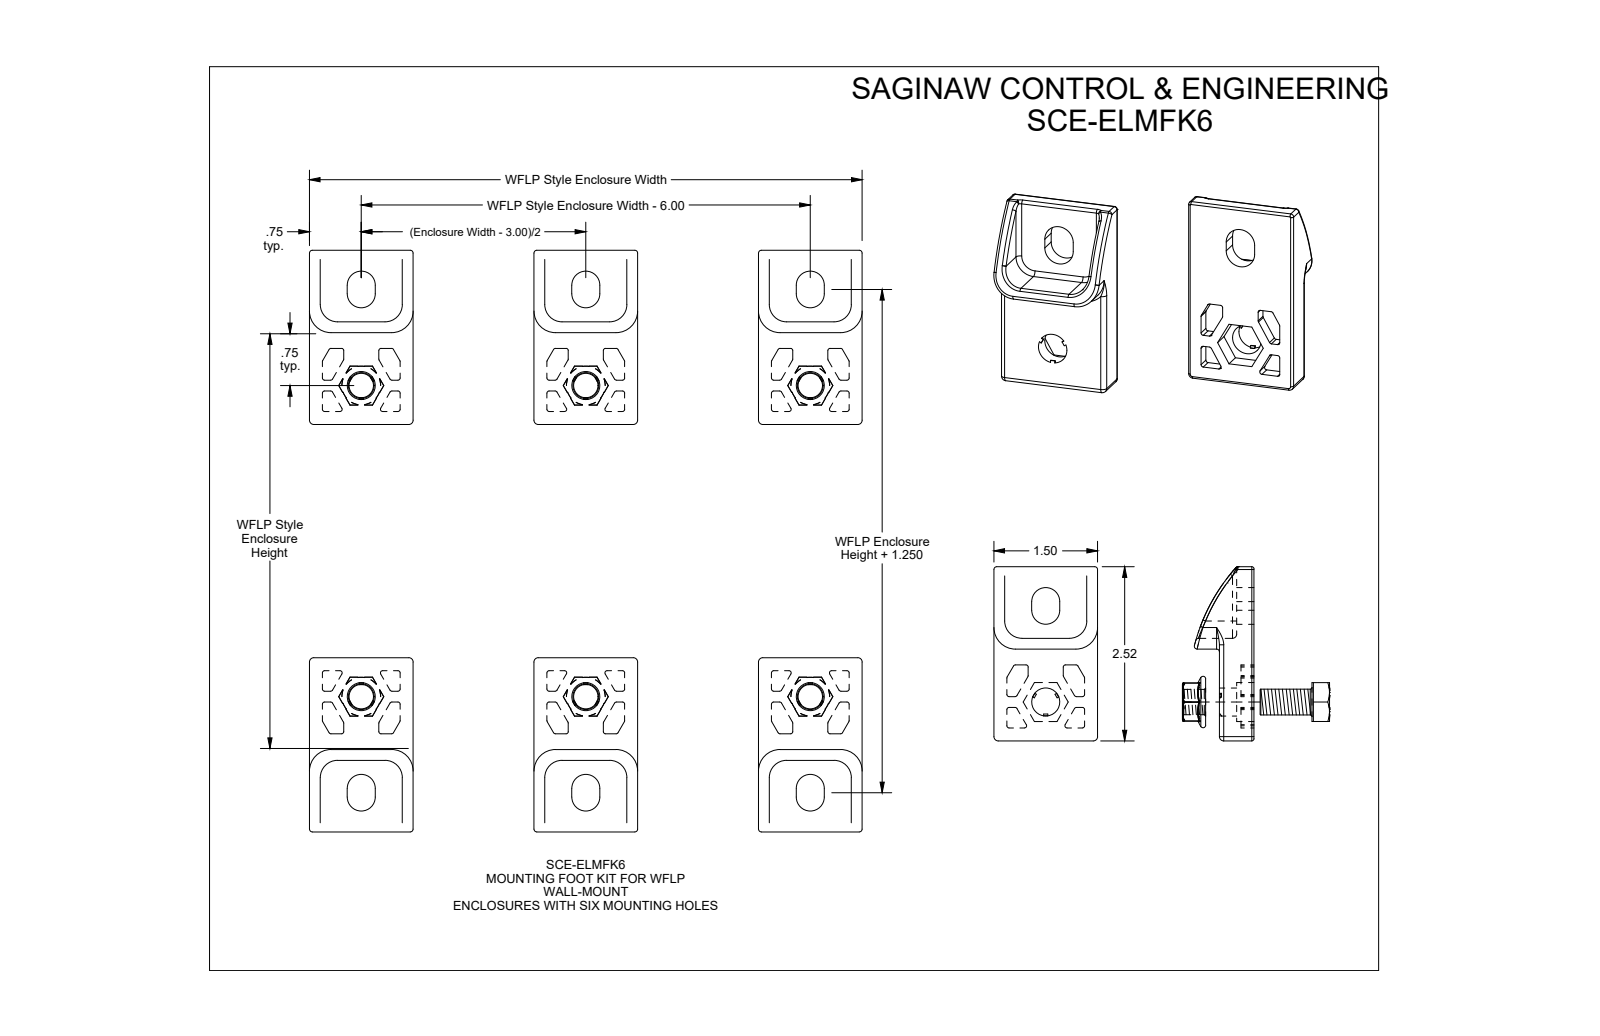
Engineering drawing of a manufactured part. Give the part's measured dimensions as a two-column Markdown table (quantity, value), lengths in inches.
| quantity | value |
| --- | --- |
| part name | SCE-ELMFK6 |
| STEP written by | SolidWorks 2019 (AUTOMOTIVE_DESIGN) |
| units | inches |
| bodies | 18 solids, 1206 faces (492 planar, 336 cylindrical, 378 other) |
| overall size | 8.415 × 8 × 1.004 |
| volume | 10.18 in³ |
| surface area | 106 in² |
| round holes (diameter × count) | 0.367 × 6, 0.406 × 6 |
| round bosses / shafts (diameter × count) | 0.563 × 6, 0.373 × 6 |
| partial cylindrical surfaces (radius × count) | 0.031 × 130, 0.01 × 36, 0.041 × 22, 0.063 × 12, 0.203 × 12, 0.25 × 12, 0.06 × 8, 0.062 × 8 |
| main face-to-face distances | 0.25, 3.25, 0.5, 1.5, 6.5, 4.75, 1.75, 0.187, 0.156, 8 |
| hole center spacings | 3.25, 5.551, 4.5, 6.5, 7.906 |
